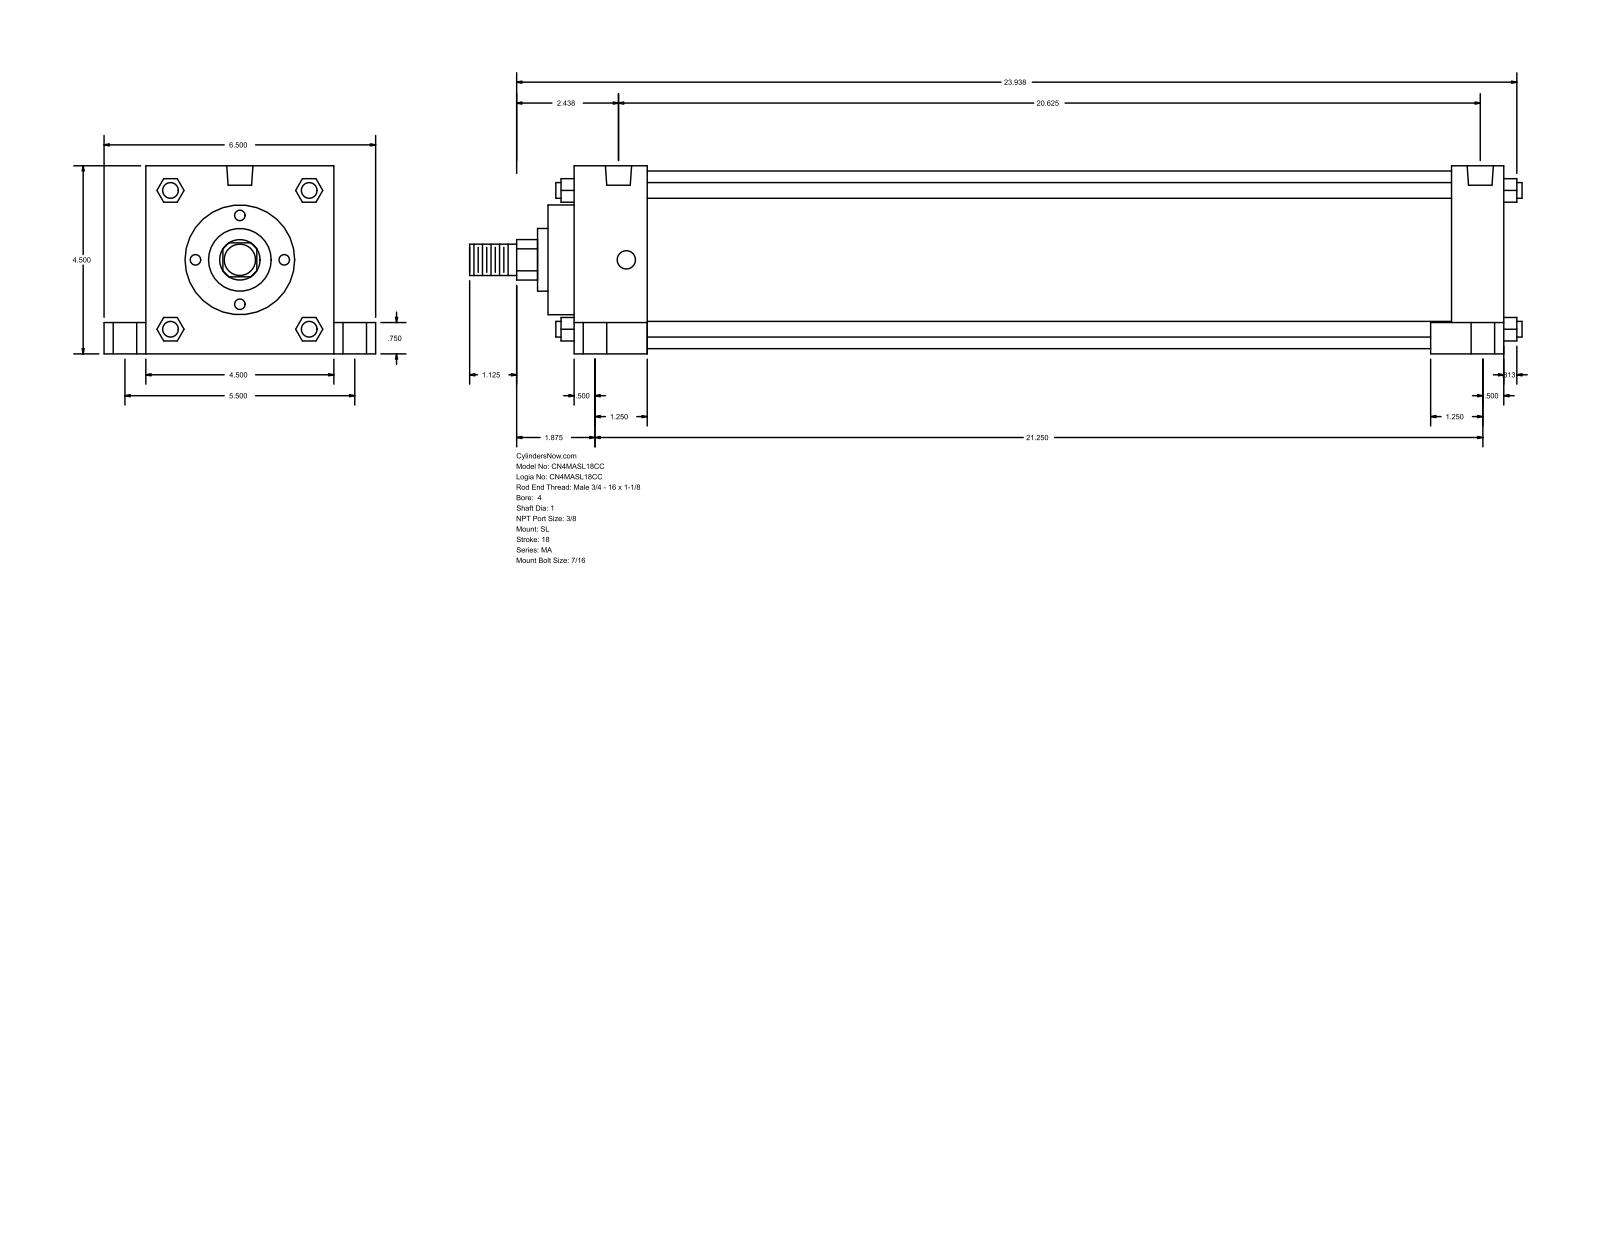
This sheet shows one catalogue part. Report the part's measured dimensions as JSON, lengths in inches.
{"part_name": "MA_SL__0400_1", "step_written_by": "GSSL Pune (CONFIG_CONTROL_DESIGN)", "units": "inches", "bodies": {"solids": 0, "faces": 150, "planar": 113, "cylindrical": 37, "other": 0}, "overall_size": [25.187, 6.5, 4.5], "round_holes": [[0.437, 4], [0.563, 4], [0.813, 4], [0.627, 2]], "round_bosses_or_shafts": [[0.375, 4], [4.25, 1], [2.625, 1], [1.5, 1], [1, 1], [0.75, 1]], "partial_cylinders_radius": [[0.484, 1]], "face_to_face_distances": [4.5, 22.25, 19.25, 1.75, 20.5, 21, 1.25, 1, 5.5, 0.75], "hole_center_spacings": [2.751, 2.761, 2.807, 2.85, 5.5, 20.25, 20.684, 20.87]}
